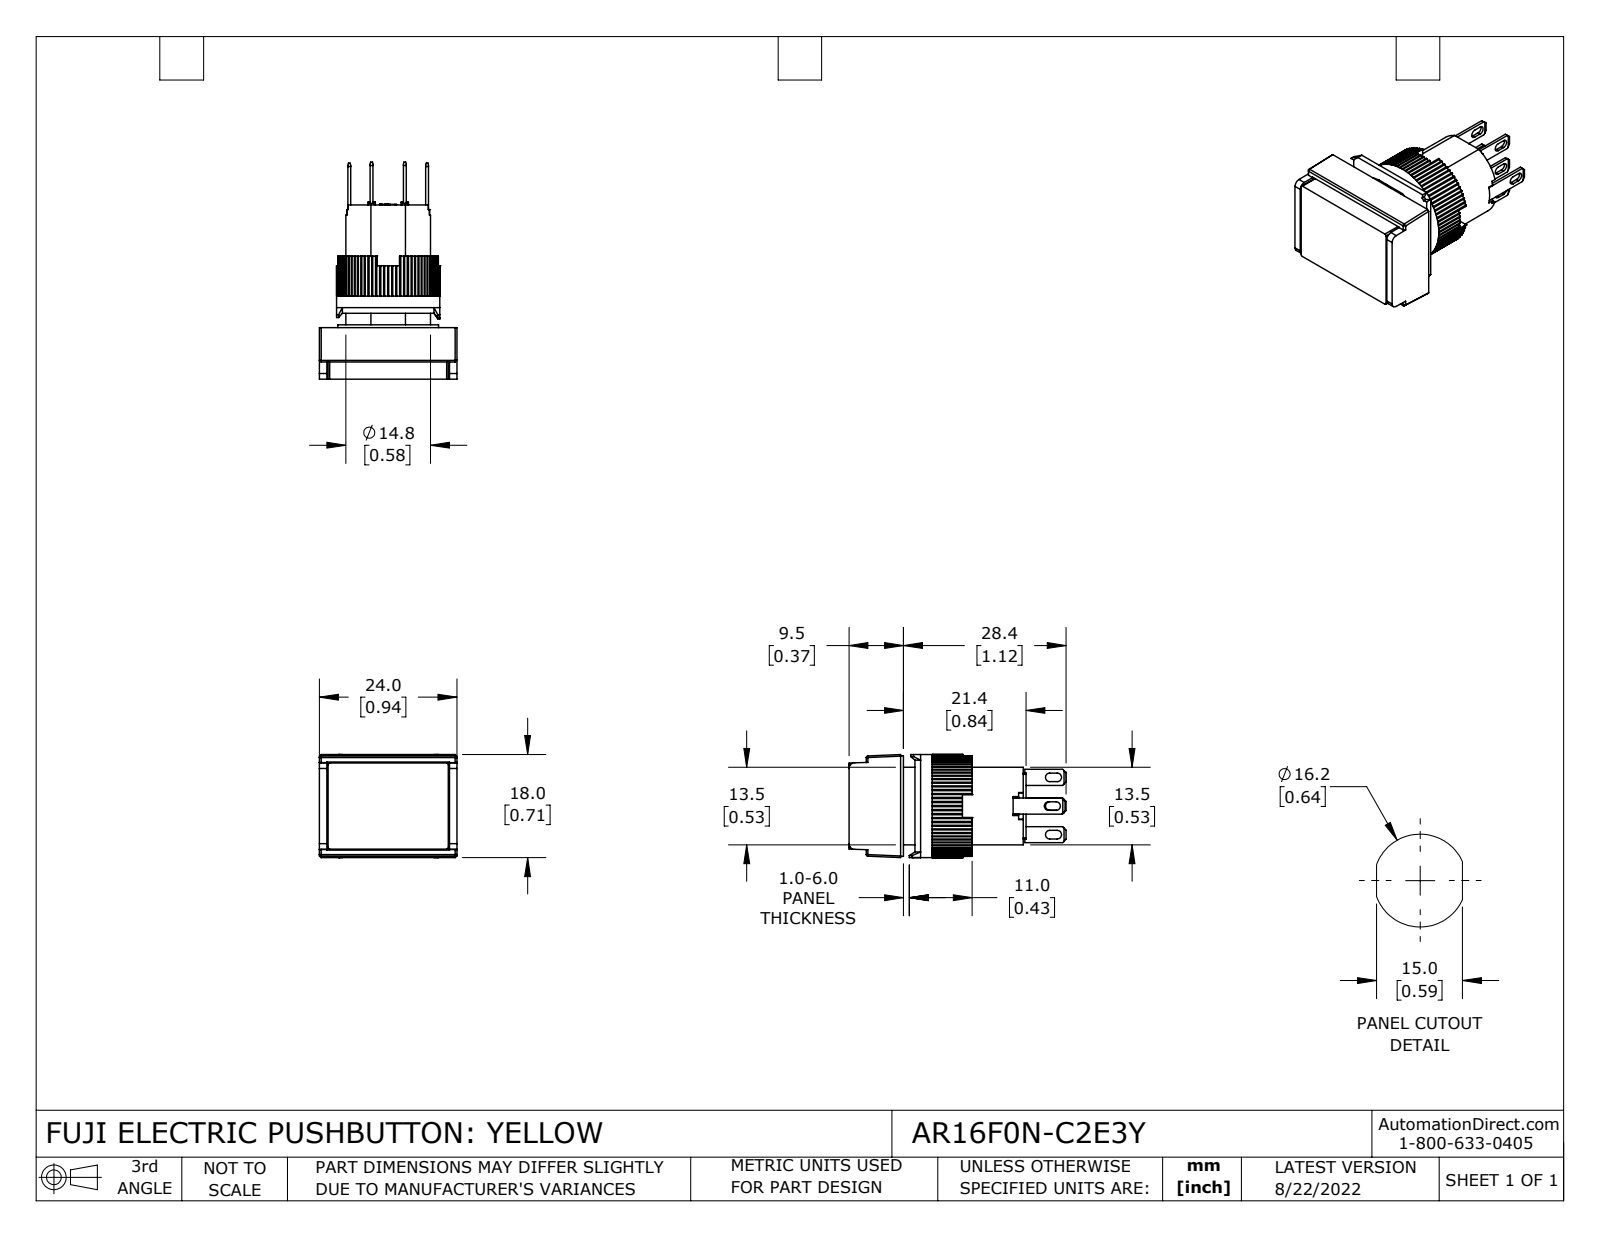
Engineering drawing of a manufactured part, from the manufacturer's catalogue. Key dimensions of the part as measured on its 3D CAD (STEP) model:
Part name (STEP PRODUCT): AR16F0N-C2E3Y
STEP written by: SolidWorks 2021 (CONFIG_CONTROL_DESIGN)
Units: inches
Bodies: 14 solids, 843 faces (656 planar, 183 cylindrical, 4 other)
Overall size (bounding box): 1.492 × 0.945 × 0.709
Volume: 0.444 in³ · Surface area: 9.306 in²
Round holes (diameter × count): ⌀0.543 ×1, ⌀0.583 ×1
Round bosses / shafts (diameter × count): ⌀0.709 ×1, ⌀0.693 ×1
Partial cylindrical surfaces — rounded edges, fillets, slot ends (radius × count): R0.01 ×80, R0.008 ×12, R0.03 ×8, R0.012 ×6, R0.039 ×2
Main face-to-face distances: 0.213, 0.354, 0.142, 0.35, 0.492, 0.138, 0.02, 0.843, 0.059, 0.453
